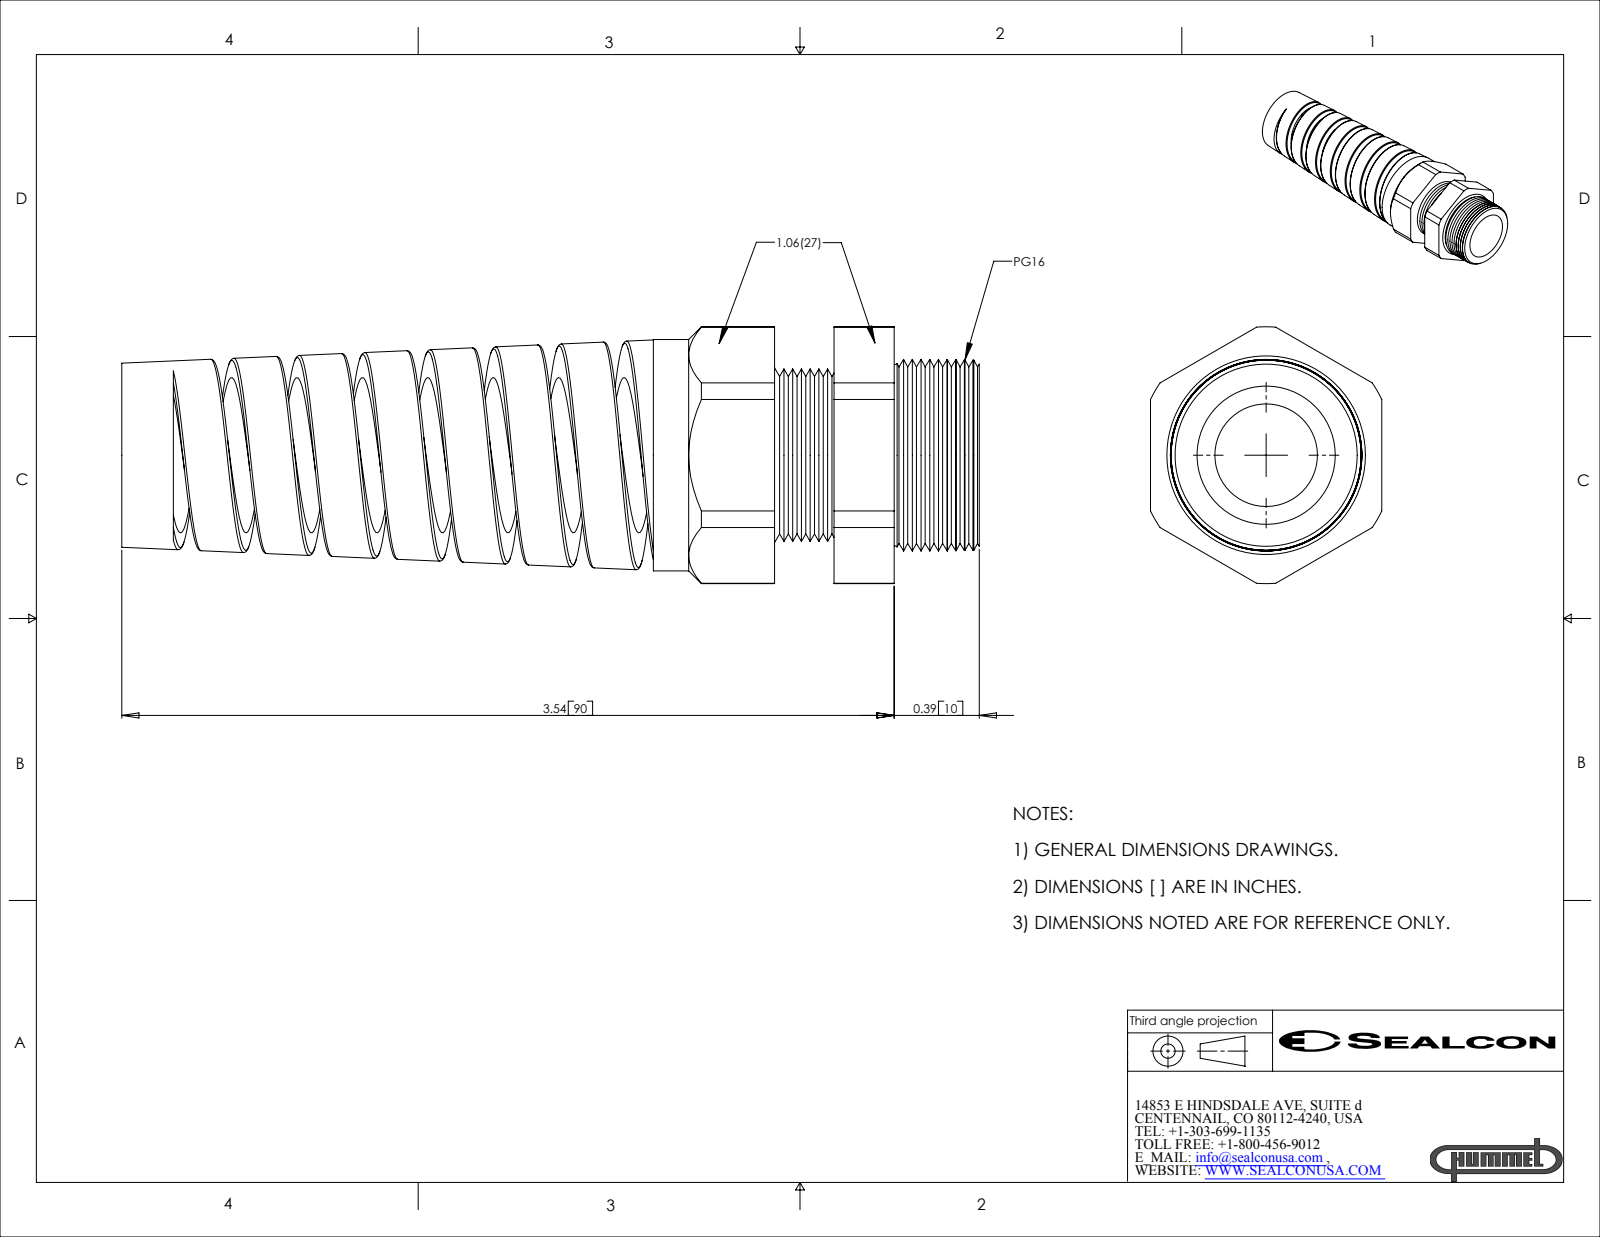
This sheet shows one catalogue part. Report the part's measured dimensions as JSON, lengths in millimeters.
{"part_name": "CF16BA-BK", "step_written_by": "SolidWorks 2007 (CONFIG_CONTROL_DESIGN)", "units": "millimeters", "bodies": {"solids": 2, "faces": 176, "planar": 24, "cylindrical": 39, "other": 113}, "overall_size": [99.8, 29.9, 26.9], "volume_mm3": 22250, "surface_area_mm2": 17880, "round_holes": [[11.9, 1], [18.1, 1], [20.3, 1]], "round_bosses_or_shafts": [[26.9, 1]], "partial_cylinders_radius": [[9.3, 1], [14.9, 1]], "face_to_face_distances": [26.9, 6.9, 13.9, 7, 23.8, 16.9, 9.9, 12.2, 19.2, 26.2]}
